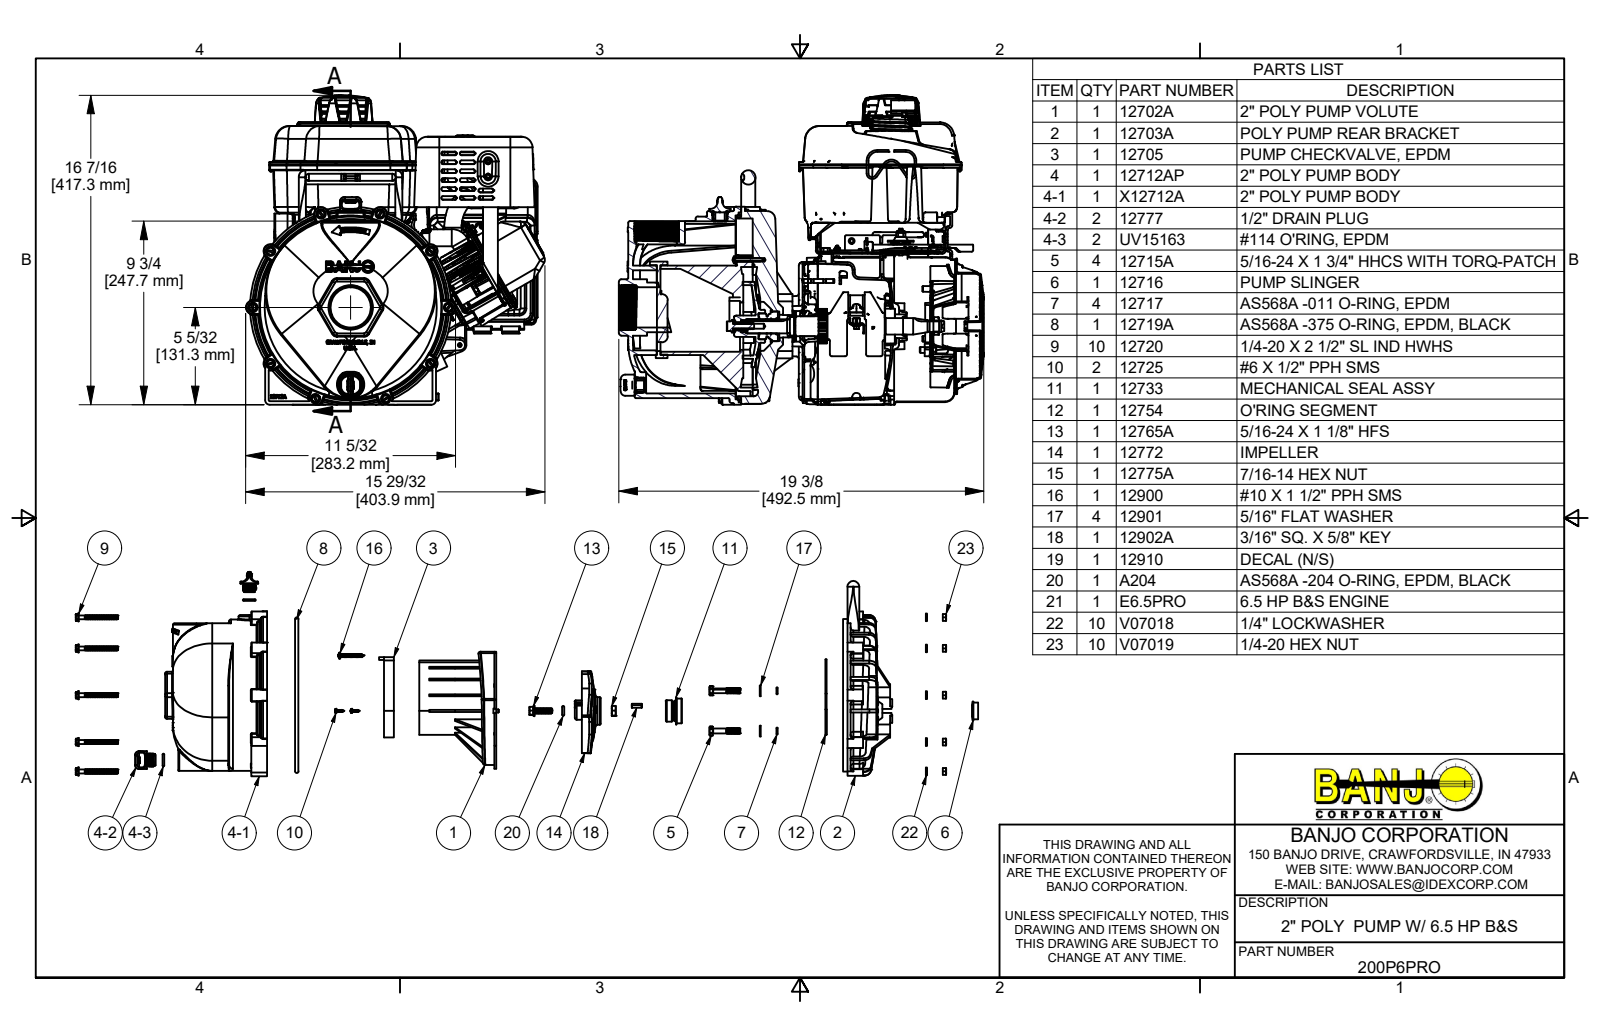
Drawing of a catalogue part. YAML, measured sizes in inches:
part_name: "200P6PRO; 12703A; 12712AP; X12712A (+8 more)"
step_written_by: "Autodesk Inventor 2019 (AUTOMOTIVE_DESIGN)"
units: inches
bodies: {solids: 84, faces: 20064, planar: 5401, cylindrical: 5558, other: 9105}
overall_size: [20.339, 17.802, 15.901]
volume: 172.7
surface_area: 4993
round_holes:
  - {diameter: 0.25, count: 13}
  - {diameter: 0.27, count: 11}
  - {diameter: 0.196, count: 10}
  - {diameter: 0.252, count: 10}
  - {diameter: 0.138, count: 9}
  - {diameter: 0.14, count: 7}
  - {diameter: 0.22, count: 7}
  - {diameter: 0.319, count: 6}
  - {diameter: 0.272, count: 5}
  - {diameter: 0.28, count: 5}
  - {diameter: 0.218, count: 4}
  - {diameter: 0.295, count: 4}
round_bosses_or_shafts:
  - {diameter: 0.276, count: 80}
  - {diameter: 0.25, count: 14}
  - {diameter: 0.5, count: 12}
  - {diameter: 0.52, count: 10}
  - {diameter: 0.489, count: 10}
  - {diameter: 0.19, count: 8}
  - {diameter: 0.276, count: 6}
  - {diameter: 0.192, count: 6}
partial_cylinders:
  - {radius: 0.06, count: 375}
  - {radius: 0.03, count: 371}
  - {radius: 0.12, count: 202}
  - {radius: 0.25, count: 110}
  - {radius: 0.09, count: 109}
  - {radius: 0.079, count: 76}
  - {radius: 0.061, count: 72}
  - {radius: 0.015, count: 71}
face_to_face_distances: [0.036, 0.18, 0.039, 0.08, 0.028, 0.2, 0.086, 8.119, 0.047, 2.88]
hole_center_spacings: [0.984, 5.2, 0.509, 1.902, 1.705, 0.561, 1.392, 1.705]
